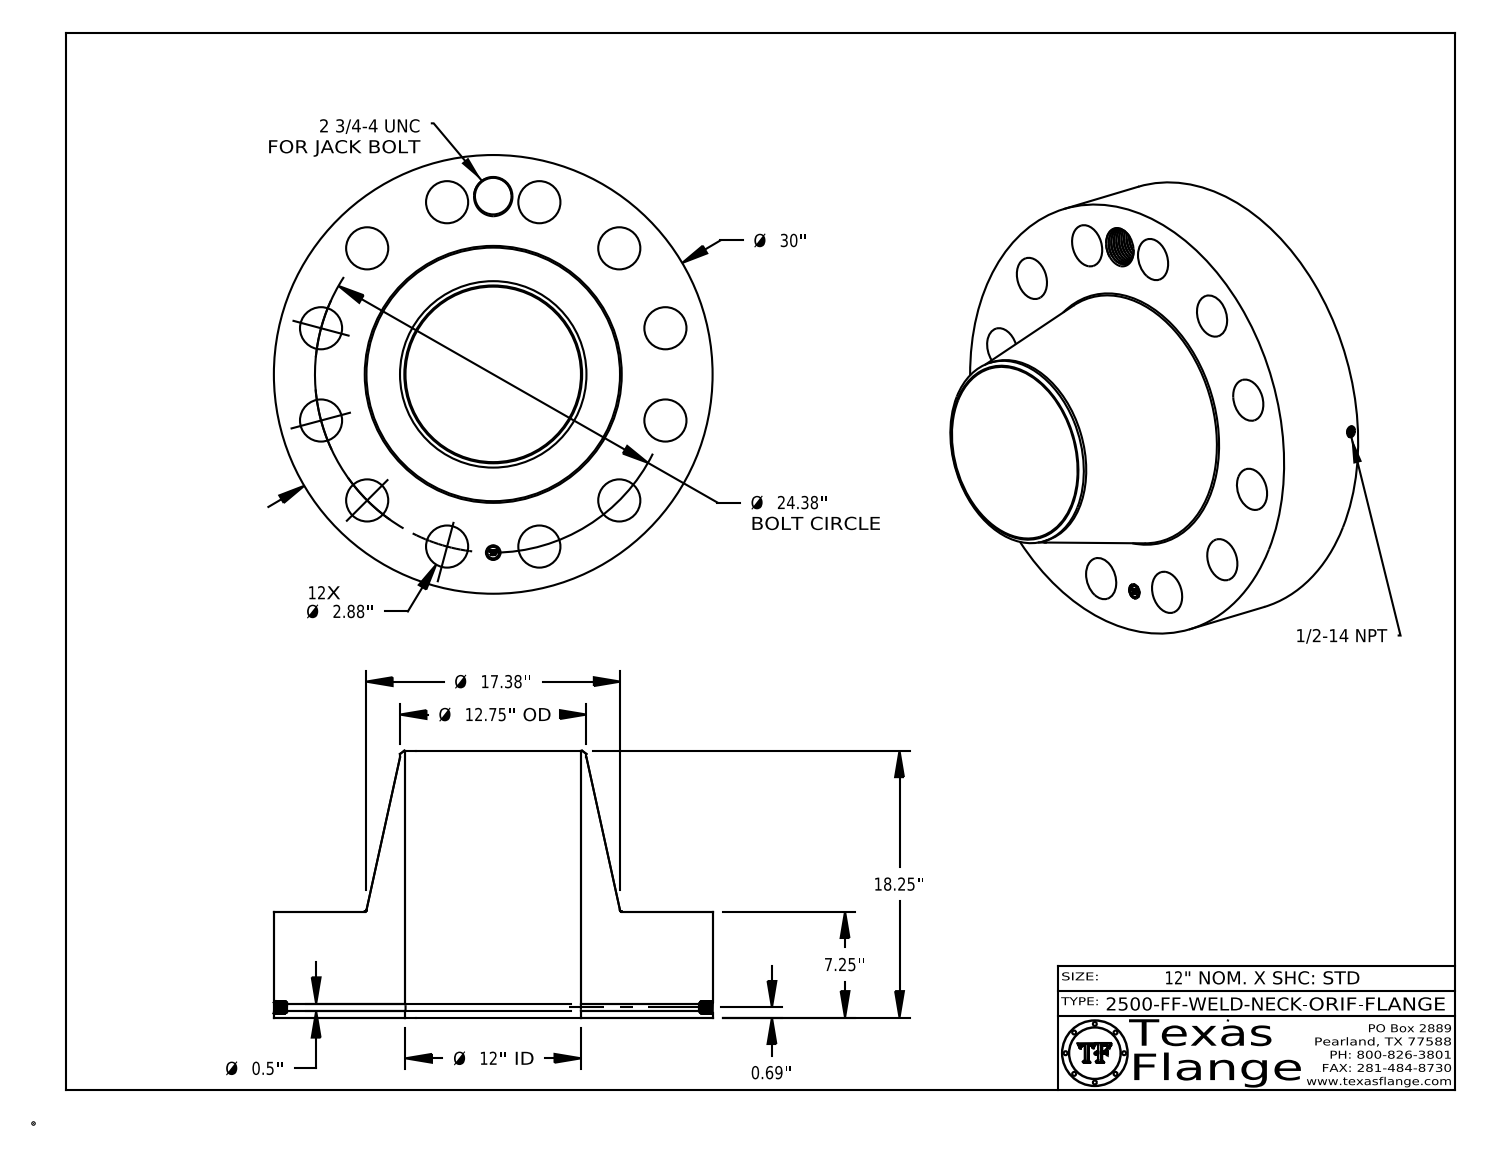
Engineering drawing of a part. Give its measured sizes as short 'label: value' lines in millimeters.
name: 2500-FF-WELD-NECK
written by: CATIA V5 STEP AP214 (AUTOMOTIVE_DESIGN)
unit: mm
bodies: 1 solid, 858 faces (368 planar, 128 cylindrical, 362 other)
size: 762 × 762 × 463.6
volume: 72 140 000 mm³; area: 2 392 000 mm²
holes: 12× ⌀73.2, 1× ⌀12.7, 1× ⌀17.1, 1× ⌀25.4, 1× ⌀63.5, 1× ⌀304.8
bosses: 8× ⌀1.5, 1× ⌀762, 1× ⌀323.9, 1× ⌀20
face distances: 184.2, 463.6, 279.4, 0.4, 183.8, 279.8, 7.6, 7.4, 1.4, 6.3
hole spacings: 309.6, 437.9, 598.2, 160.3, 536.3, 619.3, 80.8, 160.3
